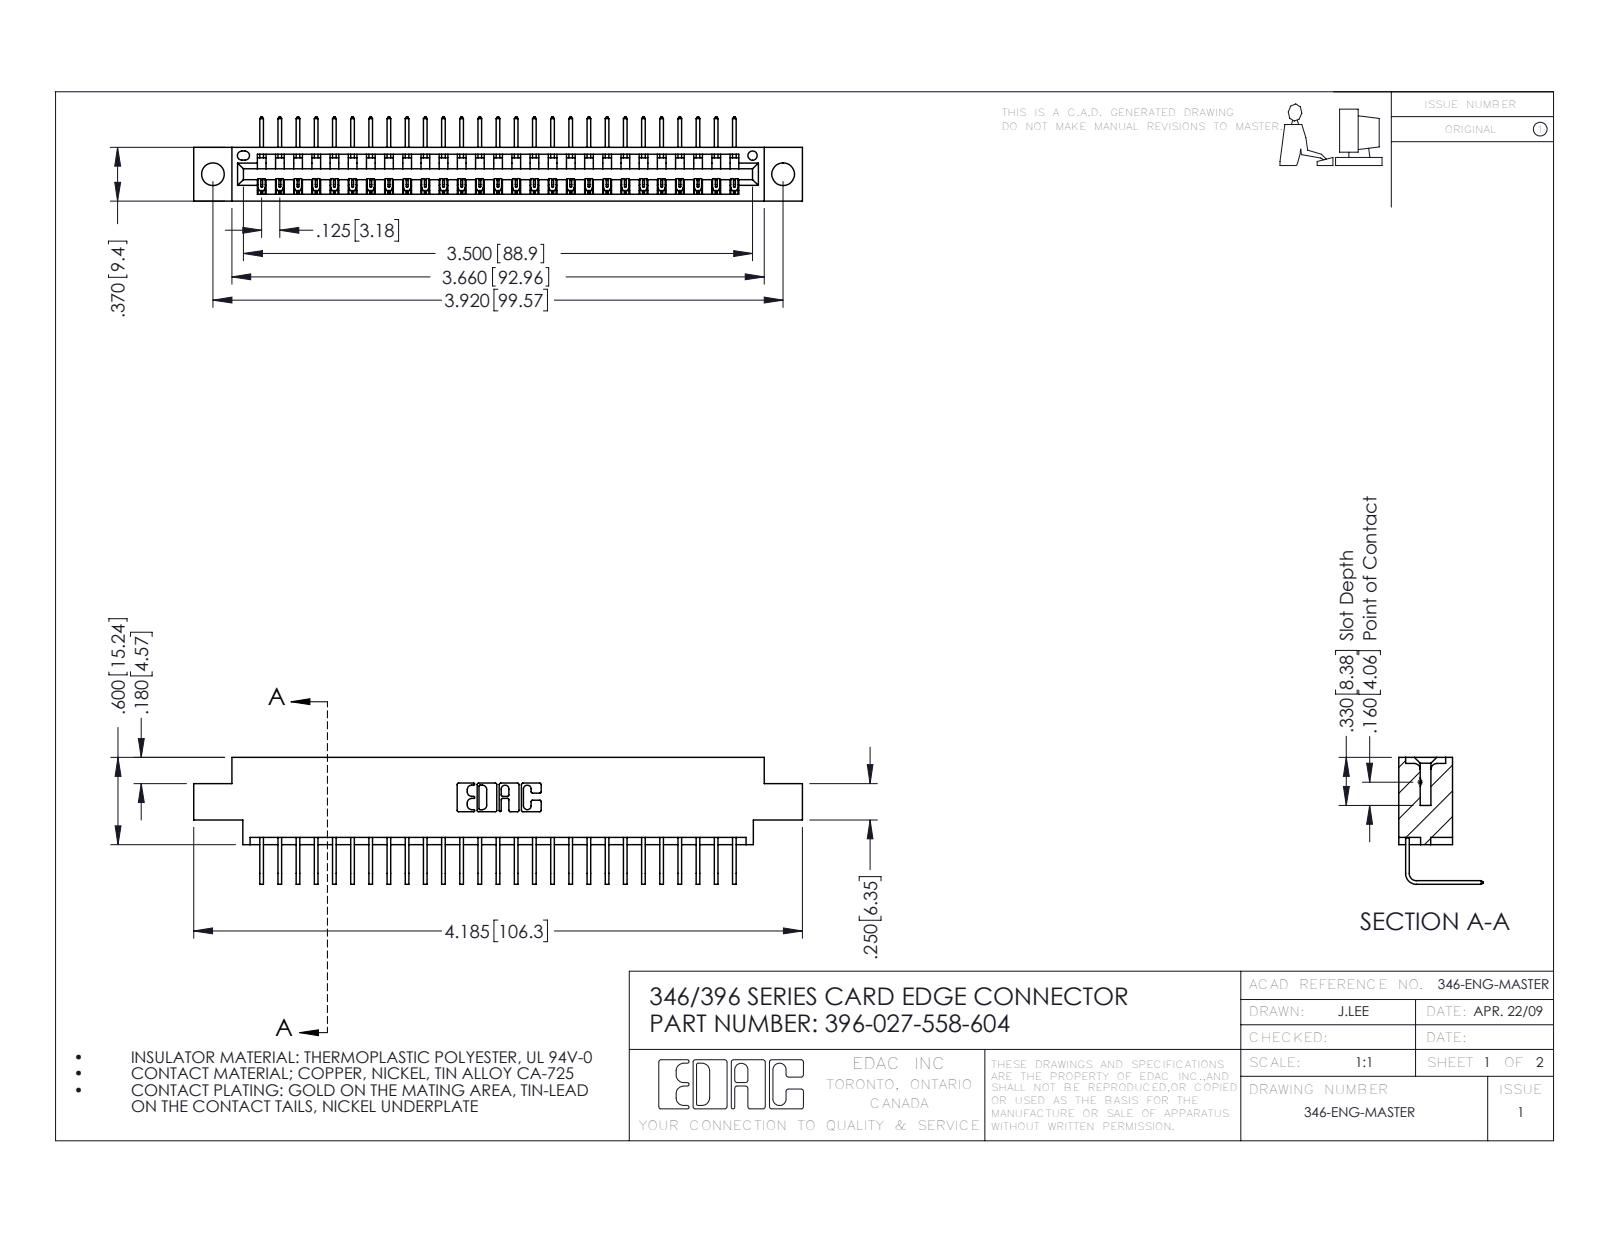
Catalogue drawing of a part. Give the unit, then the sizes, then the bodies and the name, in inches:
Units: inches
Overall size (bounding box): 4.185 × 0.873 × 0.58
Round holes (diameter × count): ⌀0.156 ×2, ⌀0.064 ×1
Partial cylindrical surfaces — rounded edges, fillets, slot ends (radius × count): R0.006 ×54, R0.01 ×22, R0.007 ×6, R0.031 ×6, R0.026 ×3, R0.031 ×2, R0.04 ×2, R0.014 ×1
Main face-to-face distances: 0.322, 0.048, 0.37, 0.25, 0.298, 0.025, 0.072, 0.148, 0.222, 0.1
Hole centre spacings: 0.246, 3.712, 3.92
Volume: 0.605 in³ · Surface area: 19.74 in²
Bodies: 28 solids, 1746 faces (1214 planar, 532 cylindrical, 0 other)
Part name (STEP PRODUCT): 396-027-558-604; 346 Part_0.170 Offset - 0.156 Dia-TH; 345-292-001_558 Tail - 2
STEP written by: SolidWorks 2016 (CONFIG_CONTROL_DESIGN)
